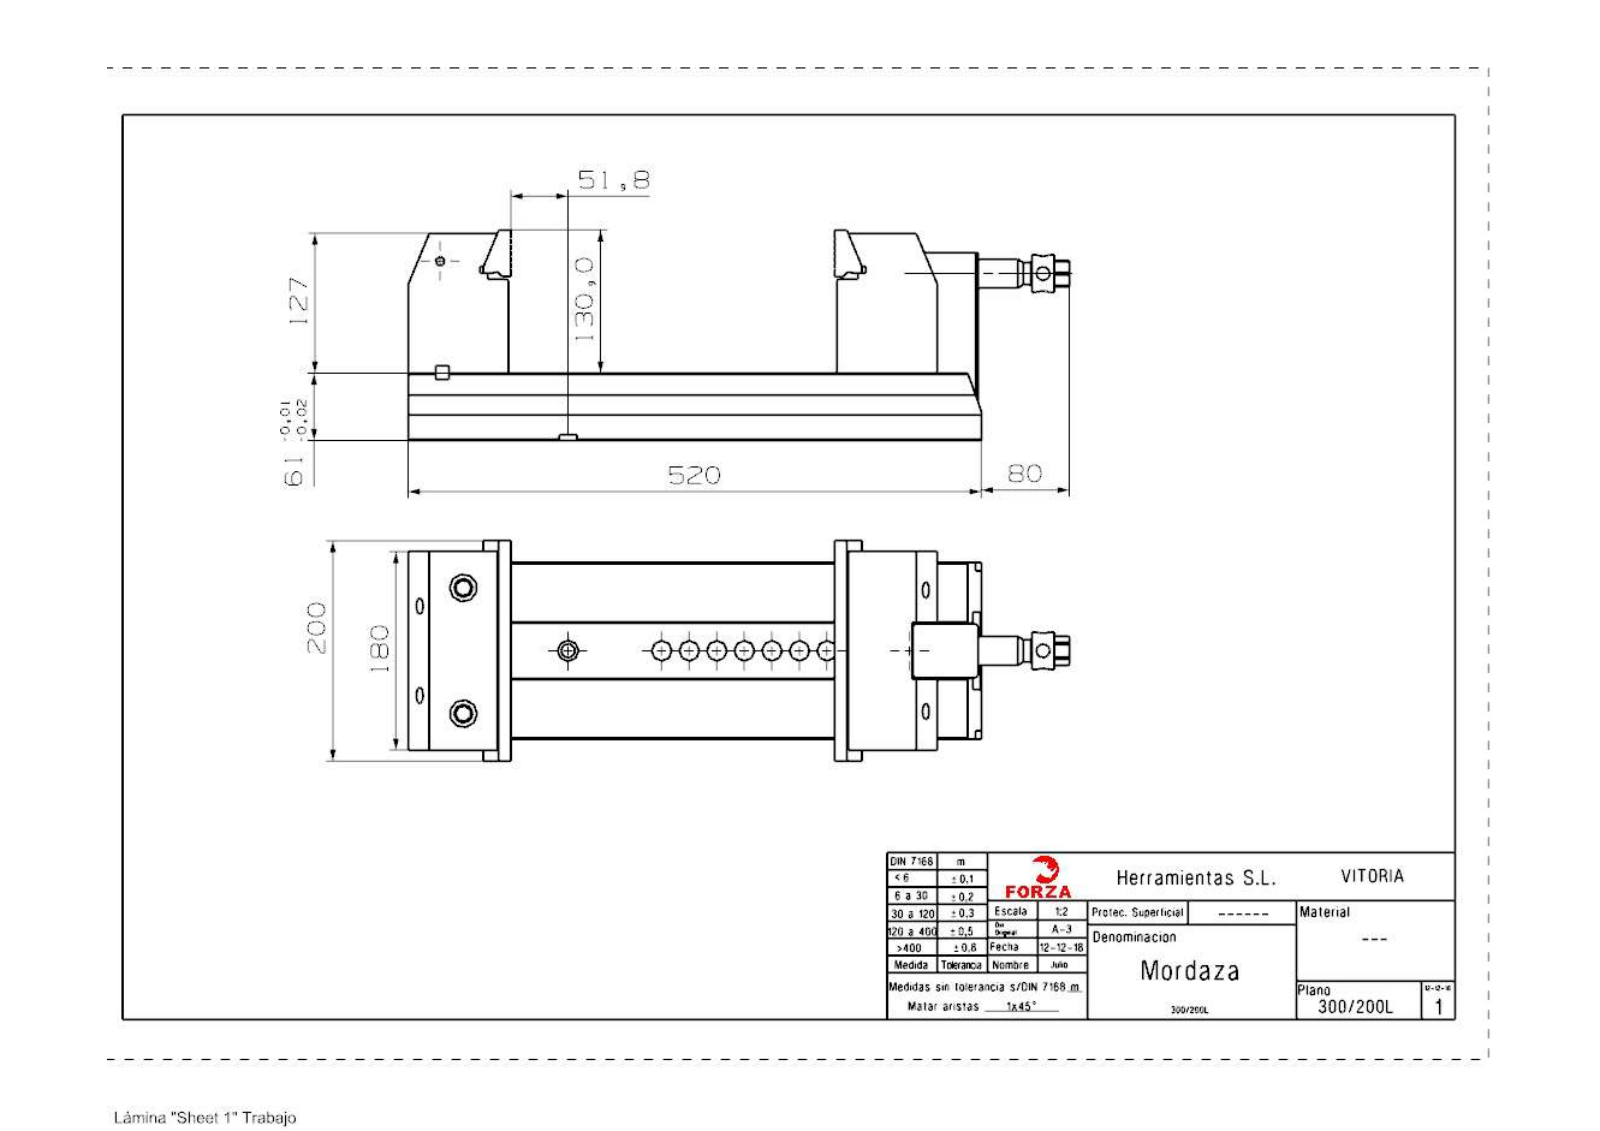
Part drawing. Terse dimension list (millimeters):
name: 300_200L_Mordaza
written by: SIEMENS PLM Software NX 11.0 (AUTOMOTIVE_DESIGN)
unit: mm
bodies: 10 solids, 472 faces (279 planar, 134 cylindrical, 59 other)
size: 600 × 200 × 191
volume: 8 065 000 mm³; area: 712 412 mm²
holes: 6× ⌀15, 5× ⌀5.19, 5× ⌀13, 5× ⌀19, 4× ⌀6.99, 4× ⌀8.5, 4× ⌀10, 3× ⌀8.78, 3× ⌀10.58, 2× ⌀12, 2× ⌀12.38, 2× ⌀14.38
bosses: 1× ⌀34, 1× ⌀33.8, 1× ⌀26, 1× ⌀20, 1× ⌀16.5
rounds: 24× R0.4, 4× R8, 4× R20, 2× R1.6, 2× R6, 2× R7, 1× R4, 1× R9
face distances: 61, 10, 170, 29.2, 31.8, 389, 91, 180, 55, 188
hole spacings: 14.5, 95.5, 81, 110, 110.72, 16.51, 16.55, 30
